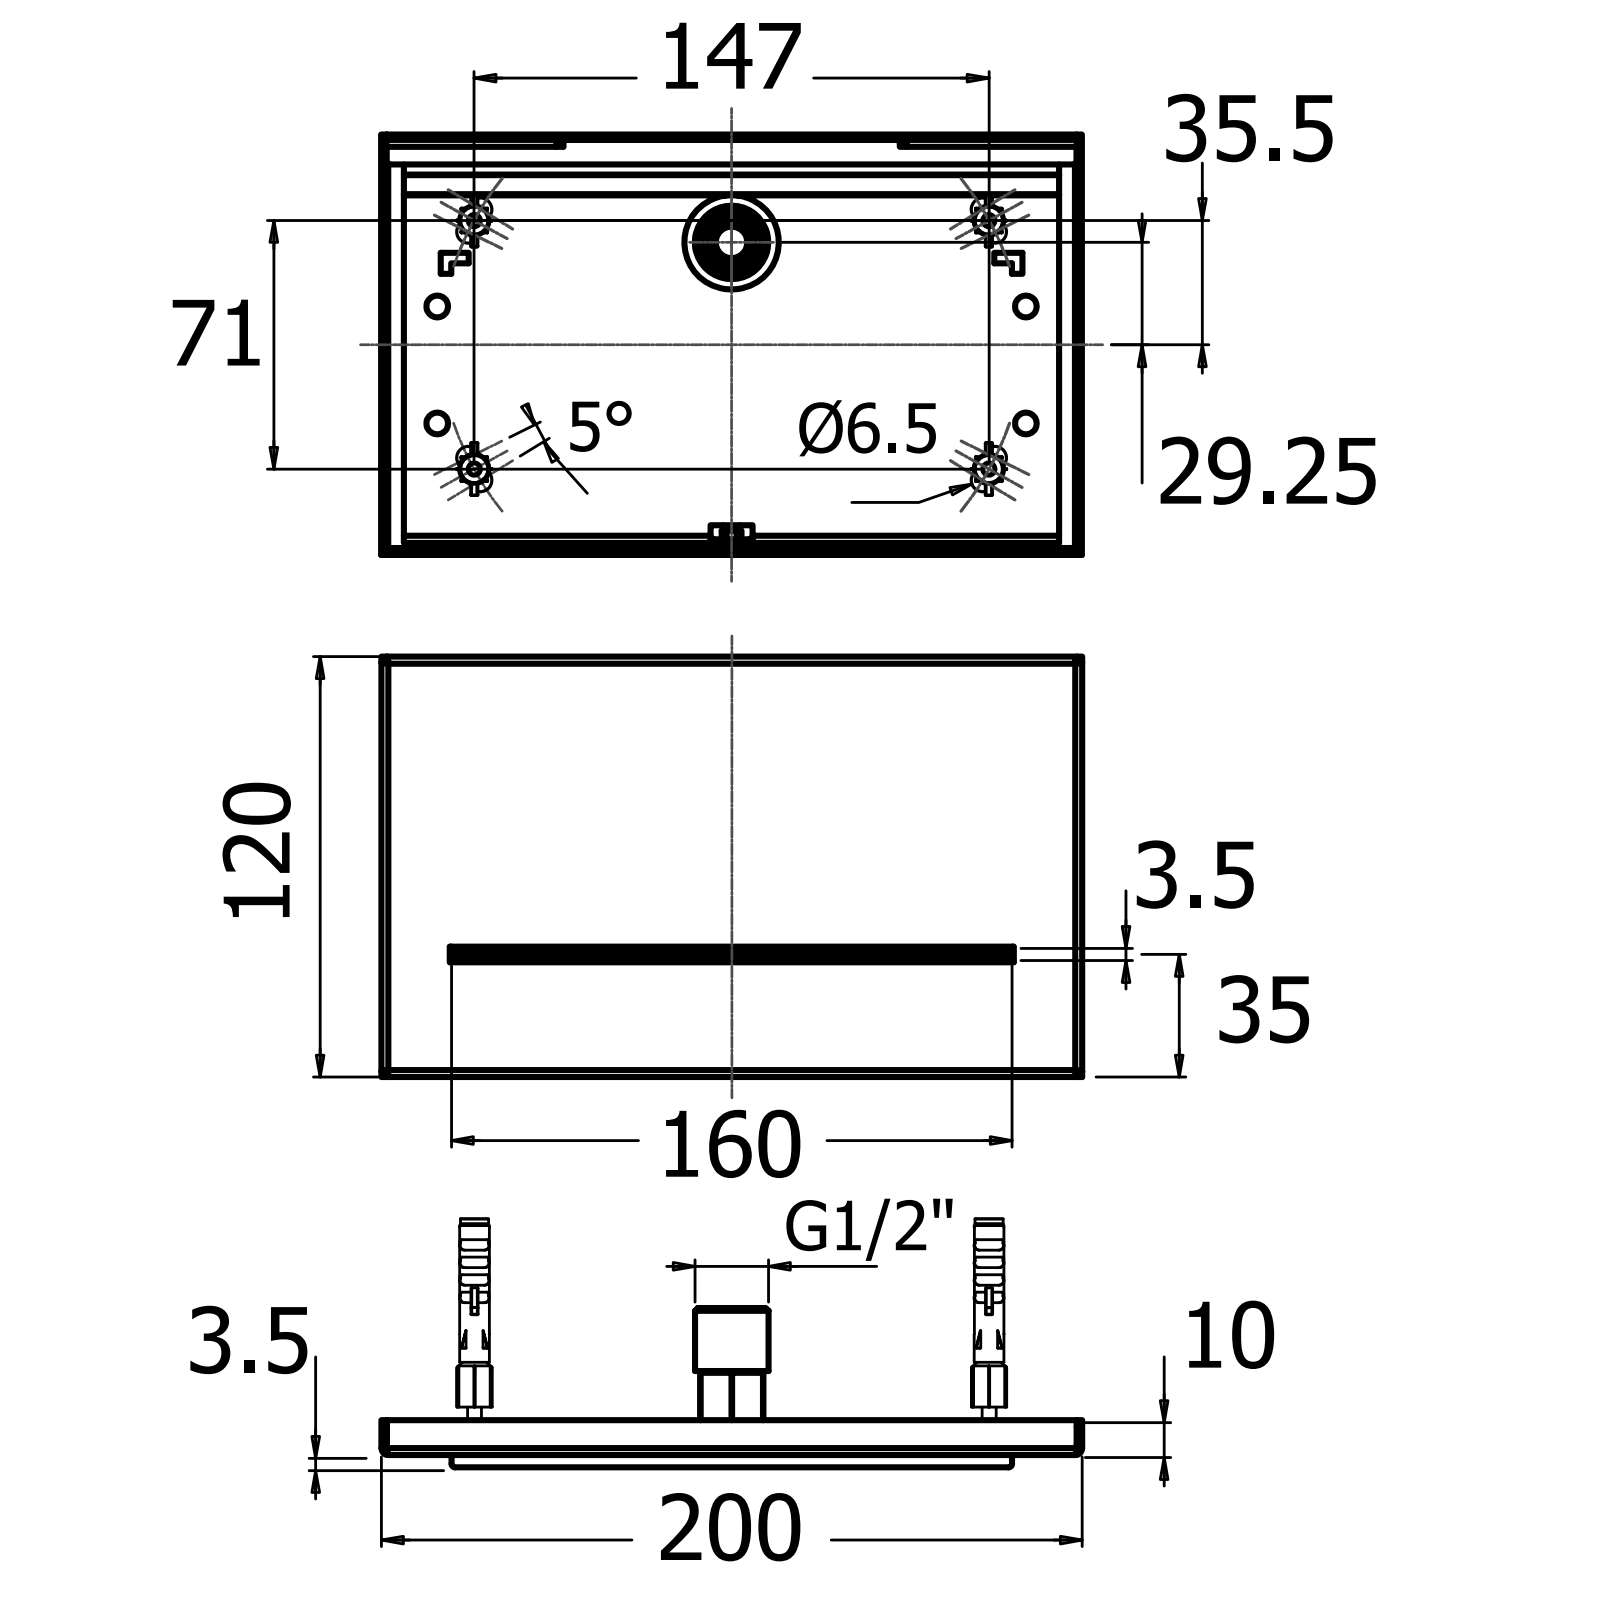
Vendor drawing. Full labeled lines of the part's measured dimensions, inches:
Part name (STEP PRODUCT): A.R._24528/20220905; Art.50002
STEP written by: Spatial InterOp 3D (AUTOMOTIVE_DESIGN)
Units: inches
Bodies: 9 solids, 521 faces (299 planar, 177 cylindrical, 45 other)
Overall size (bounding box): 7.874 × 4.724 × 1.535
Volume: 8.644 in³ · Surface area: 356.2 in²
Round holes (diameter × count): ⌀0.244 ×4, ⌀0.209 ×2, ⌀0.098 ×1, ⌀0.157 ×1, ⌀0.354 ×1, ⌀0.516 ×1, ⌀1.061 ×1
Round bosses / shafts (diameter × count): ⌀0.583 ×1, ⌀0.508 ×1, ⌀0.425 ×1, ⌀0.236 ×1, ⌀0.193 ×1, ⌀0.118 ×1, ⌀0.11 ×1
Partial cylindrical surfaces — rounded edges, fillets, slot ends (radius × count): R0.079 ×14, R0.039 ×10, R0.128 ×8, R0.004 ×4, R0.02 ×4, R0.197 ×3, R0.394 ×2, R0.787 ×2
Main face-to-face distances: 0.039, 0.059, 0.098, 0.138, 0.256, 0.394, 0.079, 0.354, 0.335, 0.295
Hole centre spacings: 0.657, 6.725, 6.693, 1.315, 3.423, 3.619, 3.917, 6.821
